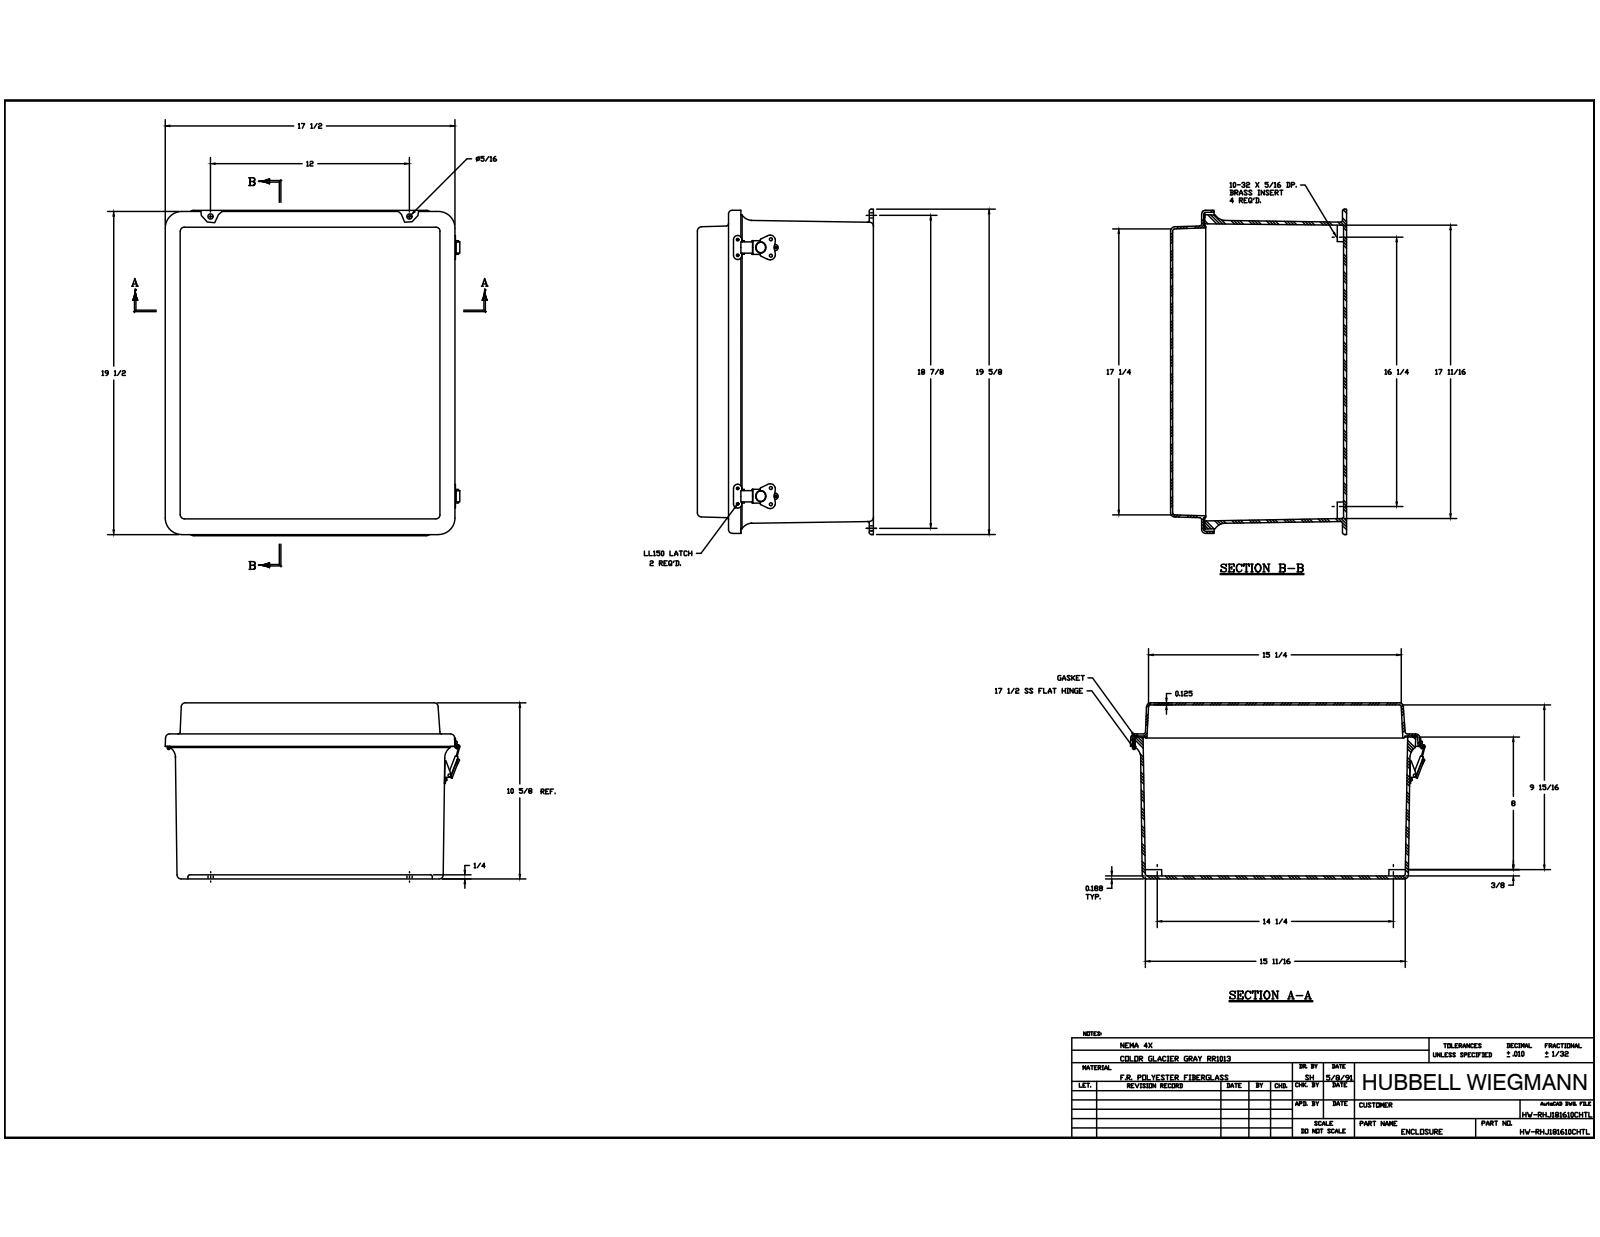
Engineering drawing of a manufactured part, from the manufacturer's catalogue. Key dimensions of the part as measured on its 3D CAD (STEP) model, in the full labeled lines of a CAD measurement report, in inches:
Part name (STEP PRODUCT): J1816HL_5; RMINS45821P_151; RMINS45821P_152; RMINS45821P_153 (+8 more)
STEP written by: Autodesk Inventor 2014 (AUTOMOTIVE_DESIGN)
Units: inches
Bodies: 52 solids, 1366 faces (620 planar, 527 cylindrical, 219 other)
Overall size (bounding box): 19.625 × 17.703 × 10.642
Volume: 249.6 in³ · Surface area: 2 947 in²
Round holes (diameter × count): ⌀0.14 ×20, ⌀0.131 ×12, ⌀0.152 ×5, ⌀0.13 ×4, ⌀0.156 ×4, ⌀0.165 ×4, ⌀0.197 ×4, ⌀0.218 ×4, ⌀0.118 ×2, ⌀0.138 ×2, ⌀0.181 ×2, ⌀0.182 ×2
Round bosses / shafts (diameter × count): ⌀0.25 ×20, ⌀0.125 ×20, ⌀0.27 ×4, ⌀0.583 ×2, ⌀0.524 ×2, ⌀0.209 ×2, ⌀0.185 ×2, ⌀0.128 ×2
Partial cylindrical surfaces — rounded edges, fillets, slot ends (radius × count): R0.031 ×20, R0.125 ×20, R0.079 ×19, R0.25 ×12, R0.037 ×8, R0.039 ×8, R0.045 ×8, R0.047 ×8
Main face-to-face distances: 0.187, 0.188, 0.125, 10.517, 10.329, 10.642, 10.454, 2, 0.125, 8.642
Hole centre spacings: 3.375, 3.375, 6.75, 14.984, 10.25, 14.984, 0.25, 9.75
